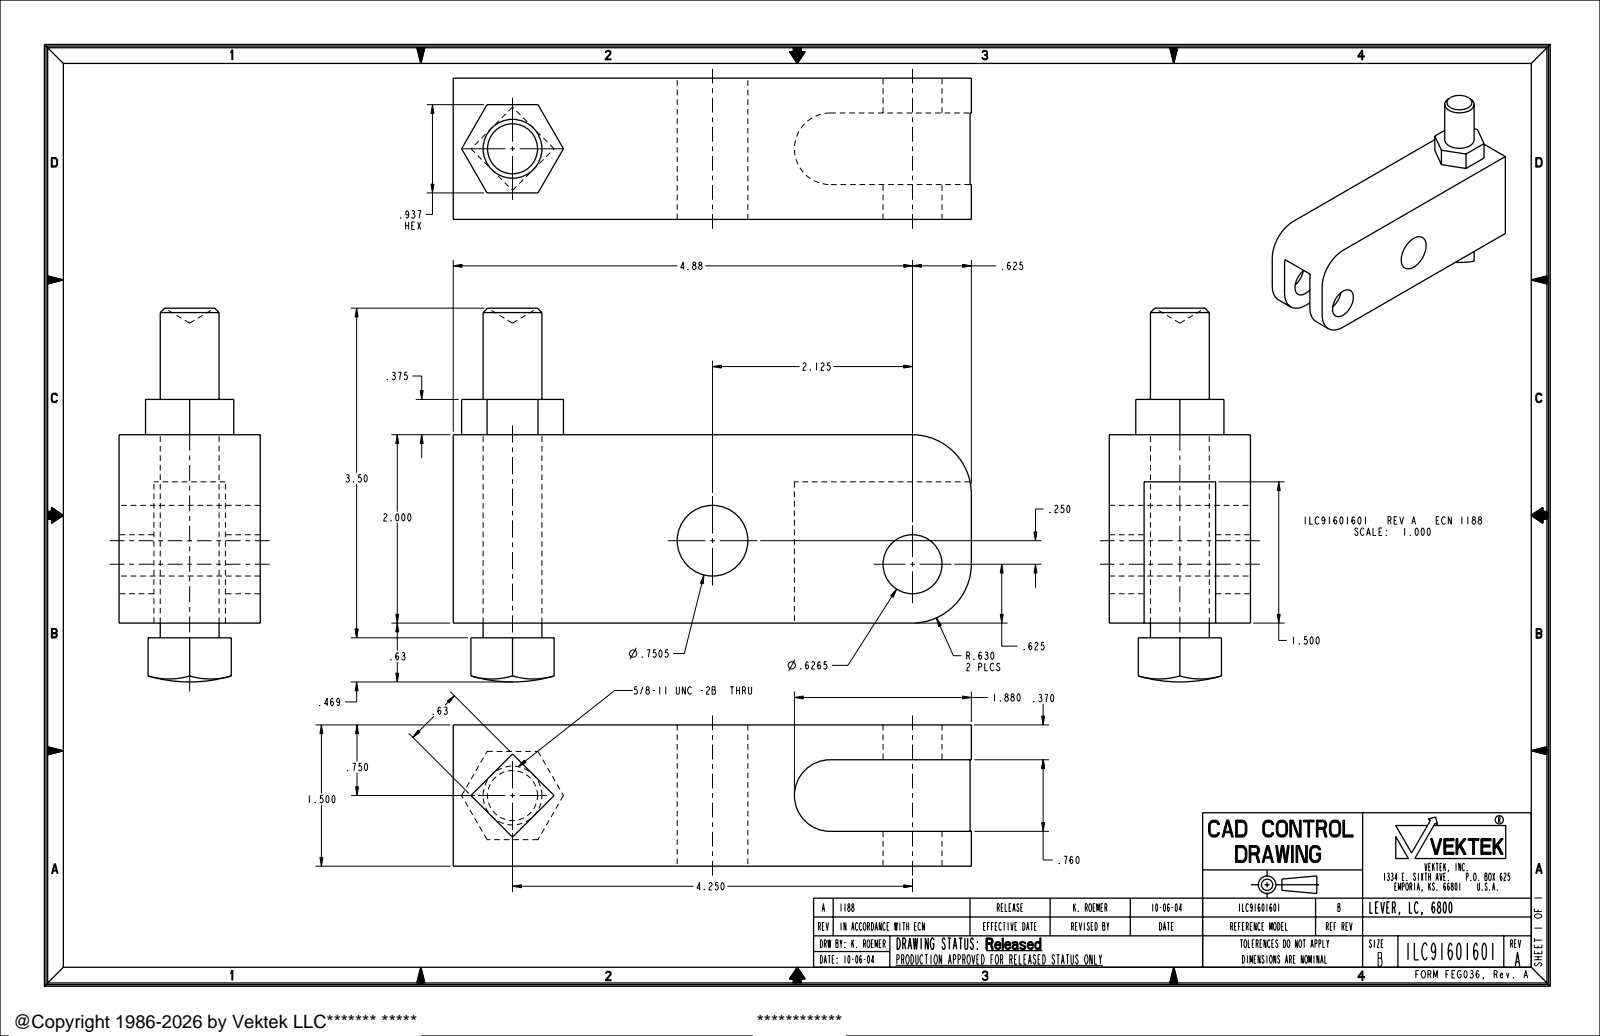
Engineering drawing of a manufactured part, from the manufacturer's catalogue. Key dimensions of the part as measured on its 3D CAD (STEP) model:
Part name (STEP PRODUCT): 91601601
STEP written by: PRO/ENGINEER BY PARAMETRIC TECHNOLOGY CORPORATION, 2004290 (CONFIG_CONTROL_DESIGN)
Units: inches
Bodies: 1 solid, 47 faces (25 planar, 16 cylindrical, 6 other)
Overall size (bounding box): 5.505 × 3.969 × 1.5
Volume: 14.17 in³ · Surface area: 60 in²
Round holes (diameter × count): ⌀0.627 ×1, ⌀0.75 ×1
Round bosses / shafts (diameter × count): ⌀0.625 ×1
Partial cylindrical surfaces — rounded edges, fillets, slot ends (radius × count): R0.63 ×2, R0.38 ×1
Main face-to-face distances: 1.5, 2, 0.37, 1.13, 0.76, 0.5, 5.505, 0.625, 2.375, 0.875
Hole centre spacings: 2.139
